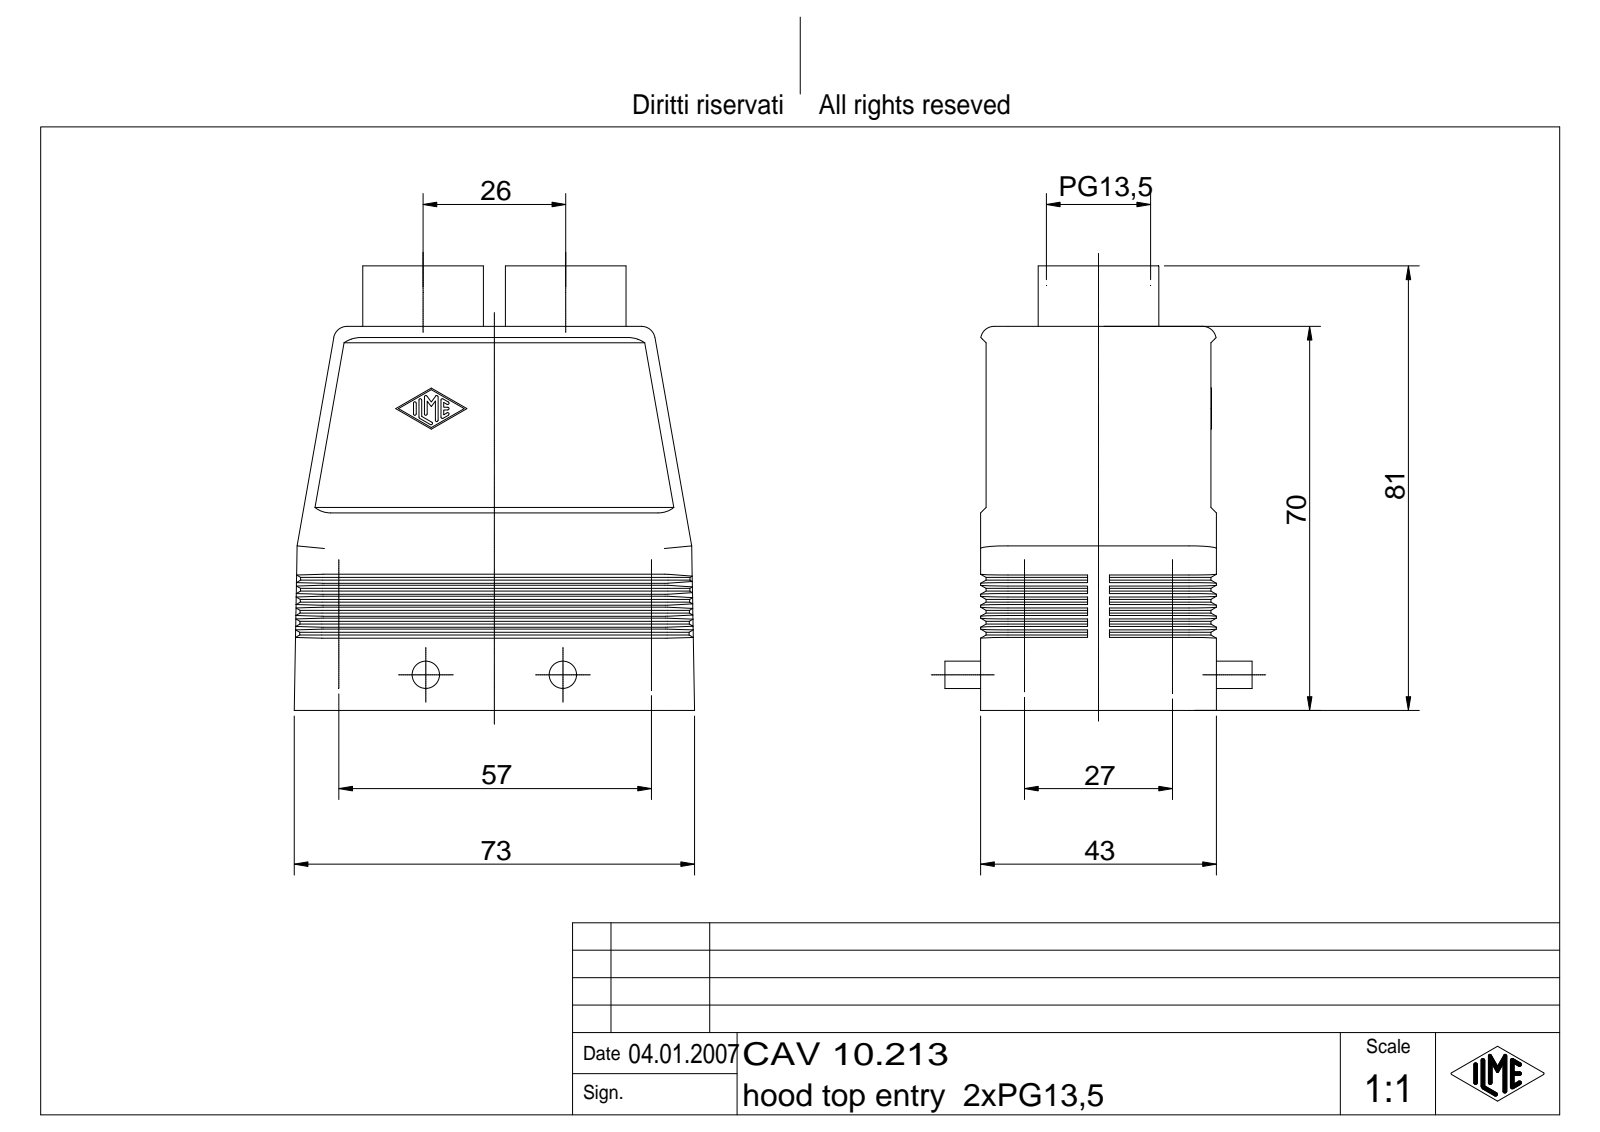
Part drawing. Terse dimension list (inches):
name: CAV 10.213
written by: Autodesk Inventor 7 (AUTOMOTIVE_DESIGN)
unit: in
bodies: 1 solid, 450 faces (148 planar, 132 cylindrical, 170 other)
size: 3.189 × 2.874 × 2.205
volume: 3.369 in³; area: 58.59 in²
holes: 2× ⌀0.669, 1× ⌀0.748, 1× ⌀0.807
bosses: 2× ⌀0.197, 1× ⌀0.866
rounds: 14× R0.01, 12× R0.157, 8× R0.079, 8× R0.197, 4× R0.098, 4× R0.138
face distances: 0.118, 0.079, 1.535, 1.457, 0.039, 1.575, 1.654, 1.614, 1.693, 0.116
hole spacings: 1.024
